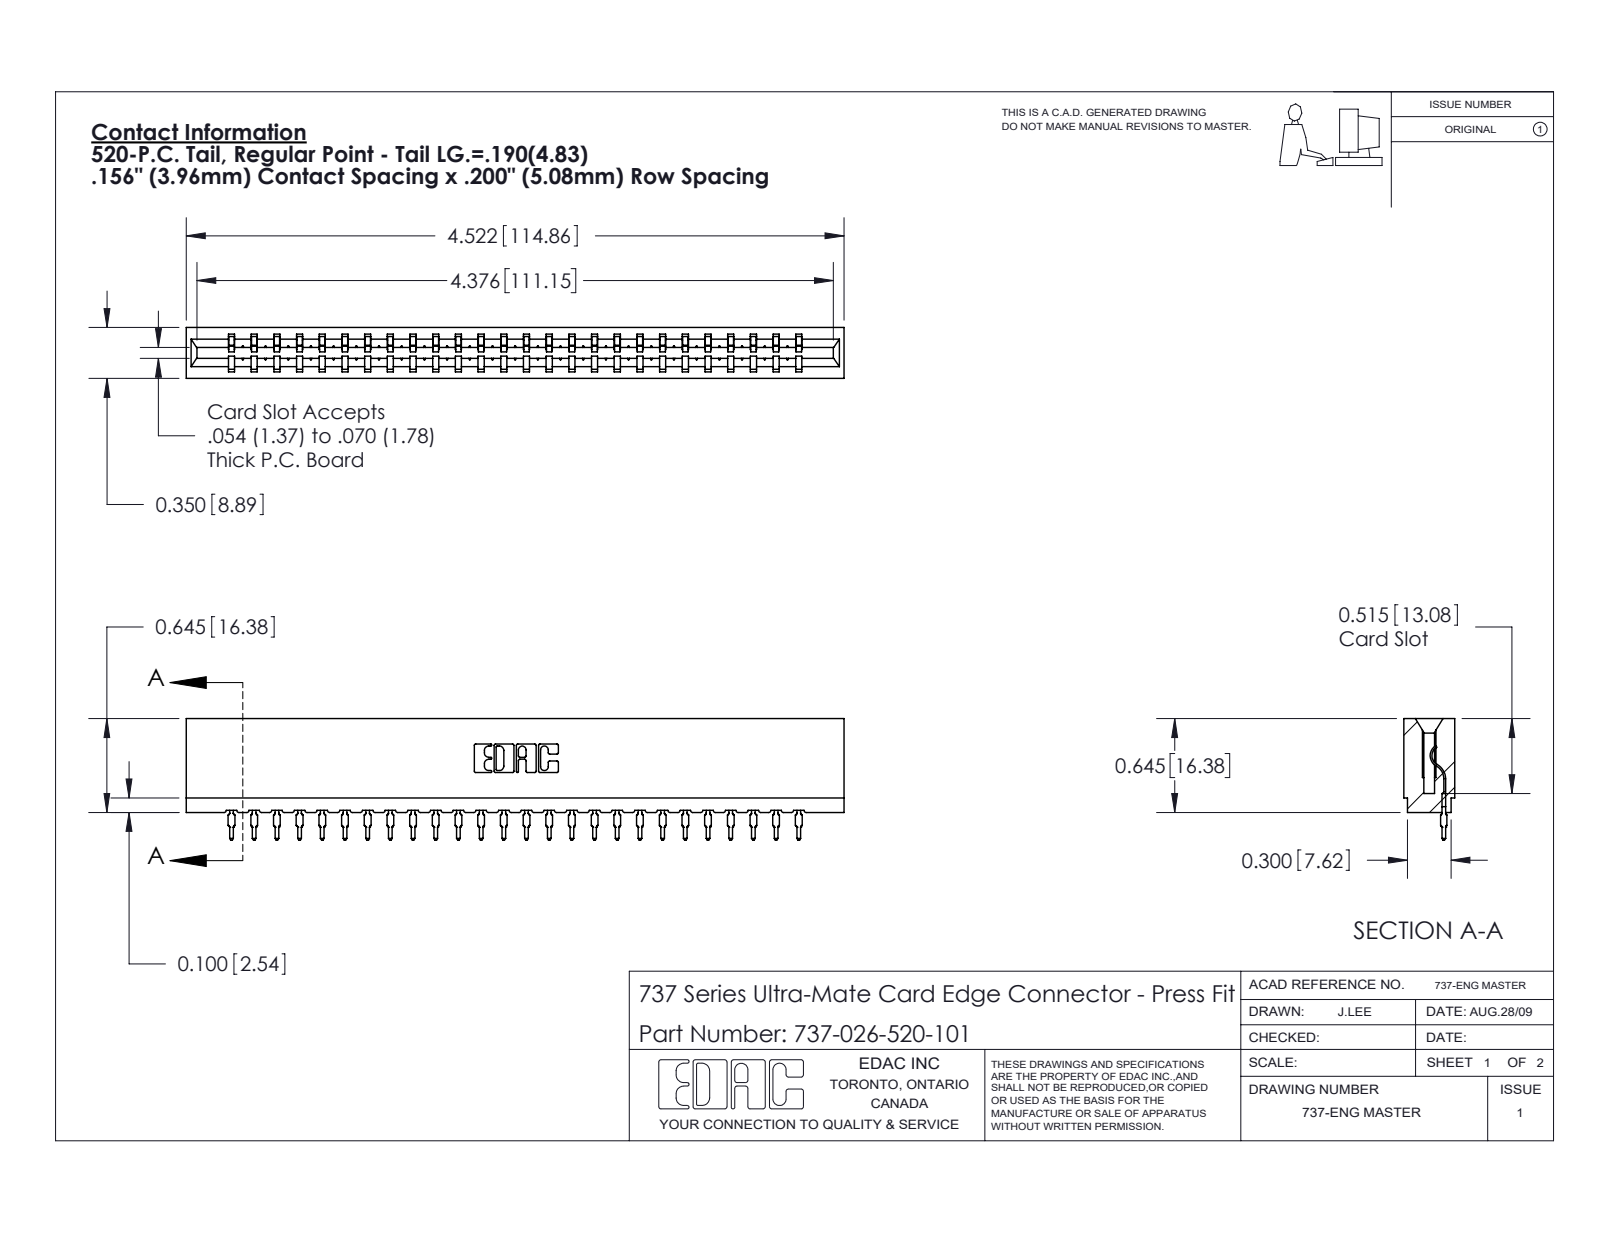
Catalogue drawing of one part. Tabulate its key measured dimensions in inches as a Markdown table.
| quantity | value |
| --- | --- |
| part name | 745-292-001_520; 737-026-520-101; 737 Part_Insulator Option - 01 |
| STEP written by | SolidWorks 2020 (CONFIG_CONTROL_DESIGN) |
| units | inches |
| bodies | 27 solids, 3032 faces (1822 planar, 534 cylindrical, 676 other) |
| overall size | 4.522 × 0.836 × 0.35 |
| volume | 0.682 in³ |
| surface area | 22.55 in² |
| partial cylindrical surfaces (radius × count) | 0.015 × 52, 0.021 × 52, 0.01 × 22, 0.007 × 6, 0.031 × 6, 0.005 × 4, 0.011 × 4, 0.026 × 3 |
| main face-to-face distances | 0.138, 0.212, 0.35, 0.156, 0.624, 0.074, 0.468, 0.78, 0.045, 0.305 |
